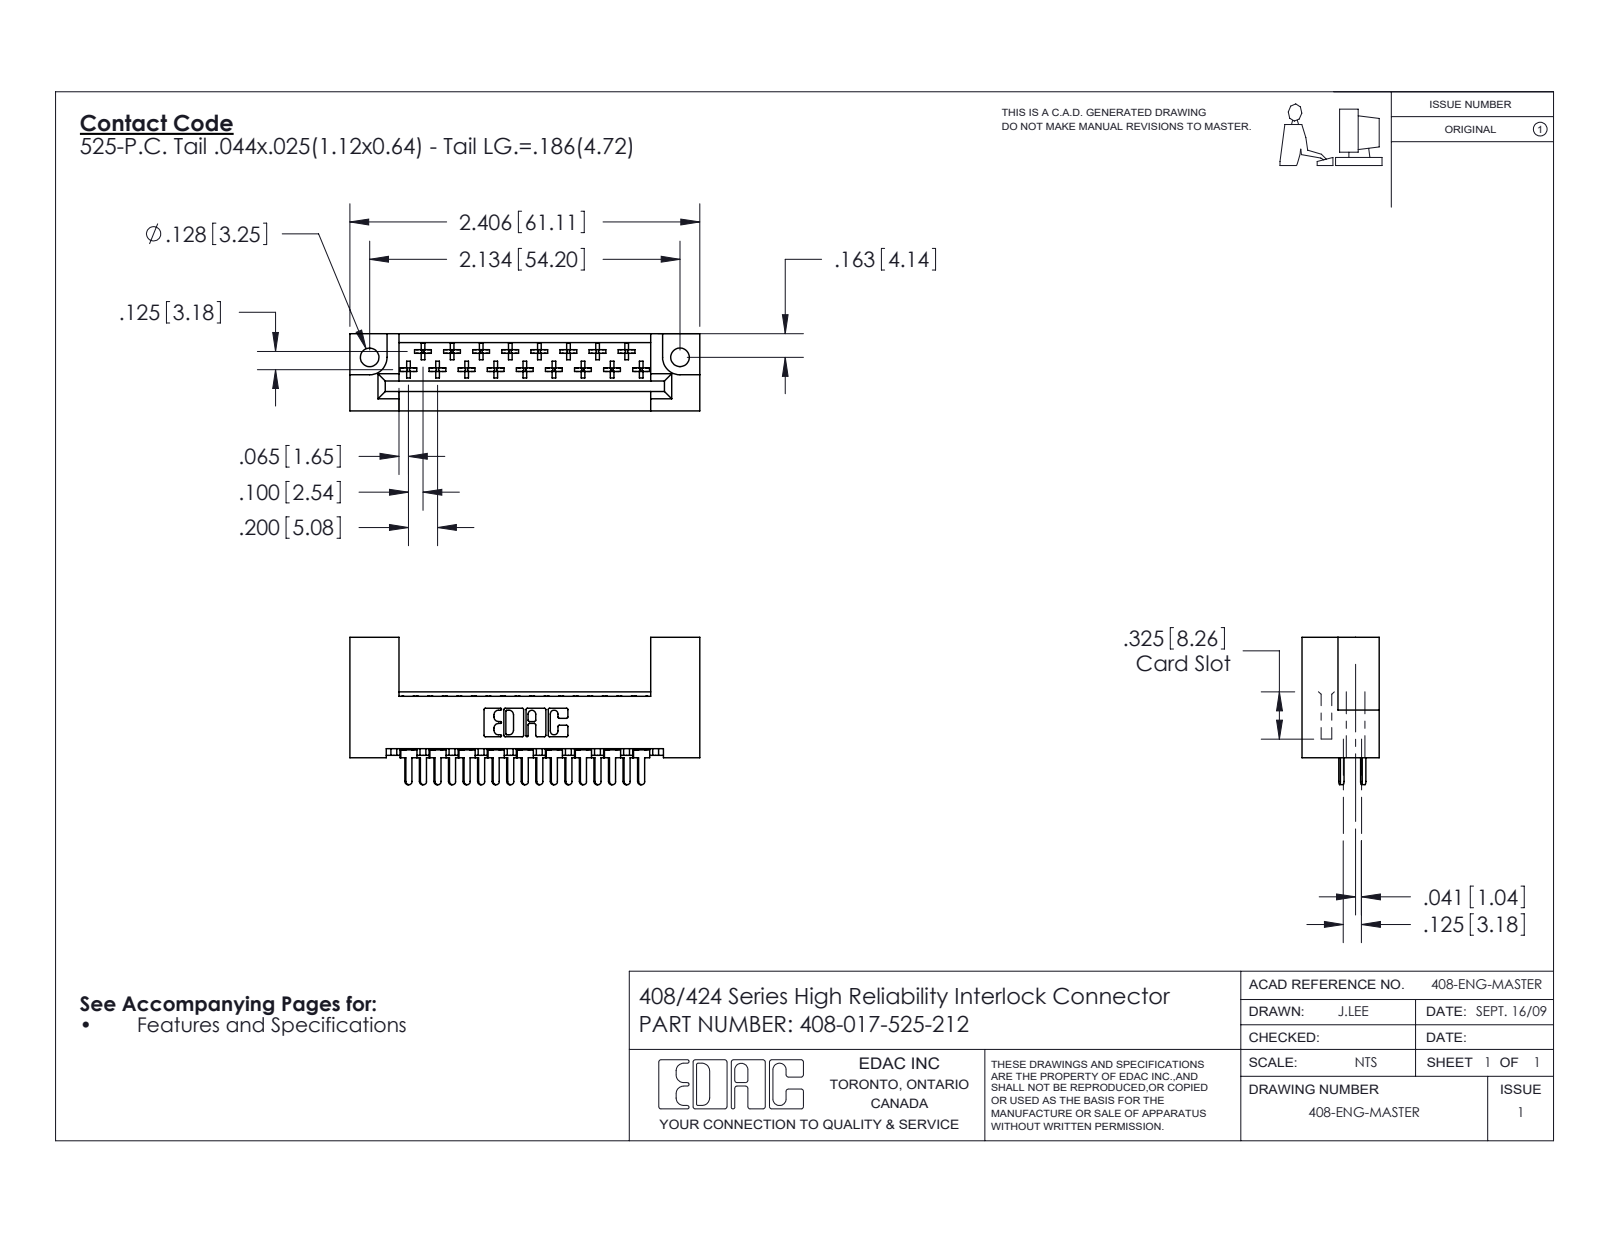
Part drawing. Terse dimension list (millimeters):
name: 408-290-001_408-290-125 - Bottom; 408-290-001_408-290-125 - Top; 408-017-525-212; 408 Part_017 - 2
written by: SolidWorks 2016 (CONFIG_CONTROL_DESIGN)
unit: mm
bodies: 18 solids, 1074 faces (803 planar, 203 cylindrical, 68 other)
size: 61.1 × 25.7 × 13.5
volume: 8 240 mm³; area: 8 806 mm²
holes: 2× ⌀3.3
rounds: 102× R0.3, 22× R0.3, 19× R0.5, 17× R0.6, 6× R0.2, 6× R0.8, 3× R0.7, 2× R3
face distances: 13.5, 3.2, 0.6, 2.5, 0.6, 10.1, 8.3, 9.2, 1.8, 5.2
hole spacings: 54.2
